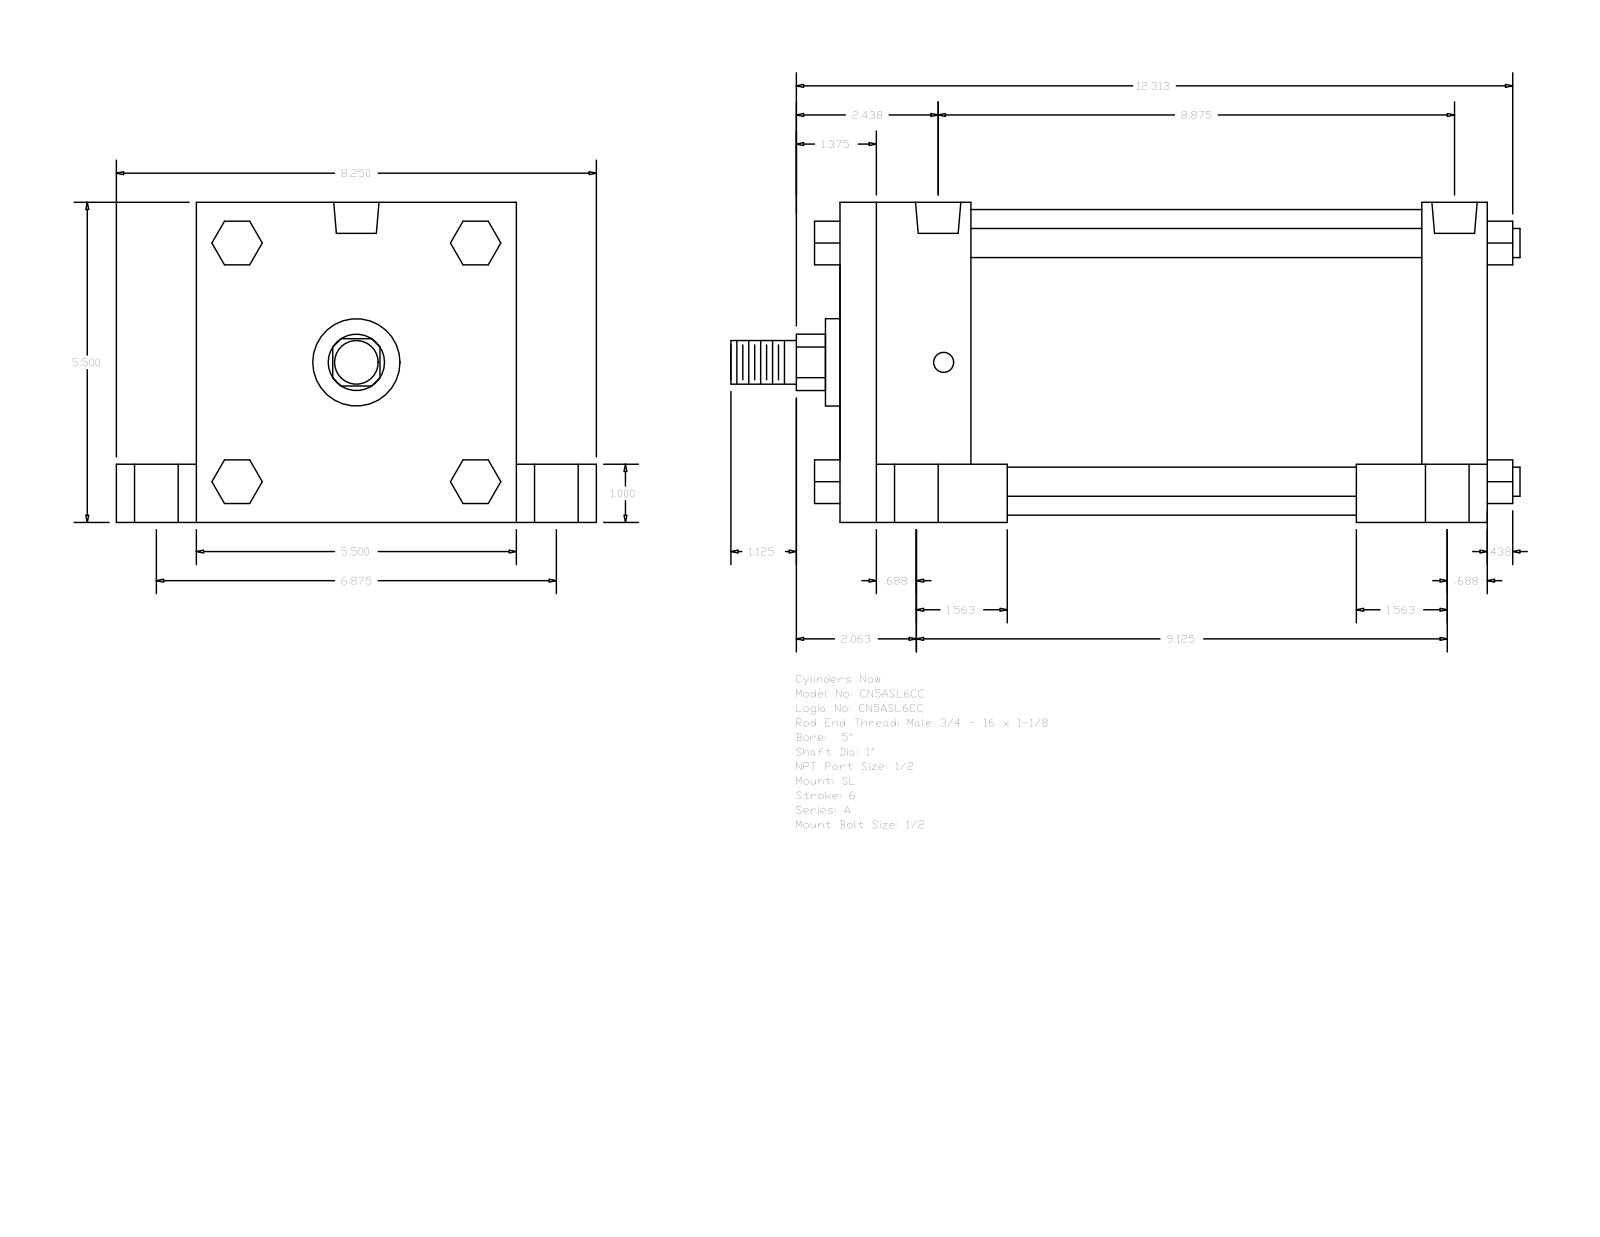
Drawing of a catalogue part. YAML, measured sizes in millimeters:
part_name: "A_SL__0500_1"
step_written_by: "GSSL Pune (CONFIG_CONTROL_DESIGN)"
units: millimeters
bodies: {solids: 0, faces: 150, planar: 114, cylindrical: 36, other: 0}
overall_size: [344.49, 209.55, 139.7]
round_holes:
  - {diameter: 8.73, count: 4}
  - {diameter: 19.05, count: 4}
  - {diameter: 25.4, count: 4}
  - {diameter: 19.77, count: 2}
round_bosses_or_shafts:
  - {diameter: 12.7, count: 4}
  - {diameter: 133.35, count: 1}
  - {diameter: 38.1, count: 1}
  - {diameter: 25.4, count: 1}
  - {diameter: 19.05, count: 1}
partial_cylinders:
  - {radius: 12.29, count: 1}
face_to_face_distances: [139.7, 282.57, 57.15, 225.42, 25.4, 114.3, 34.93, 174.63, 28.57, 254]
hole_center_spacings: [2.39, 87.31, 87.37, 87.83, 88.12, 174.62, 220.65, 223.04]
